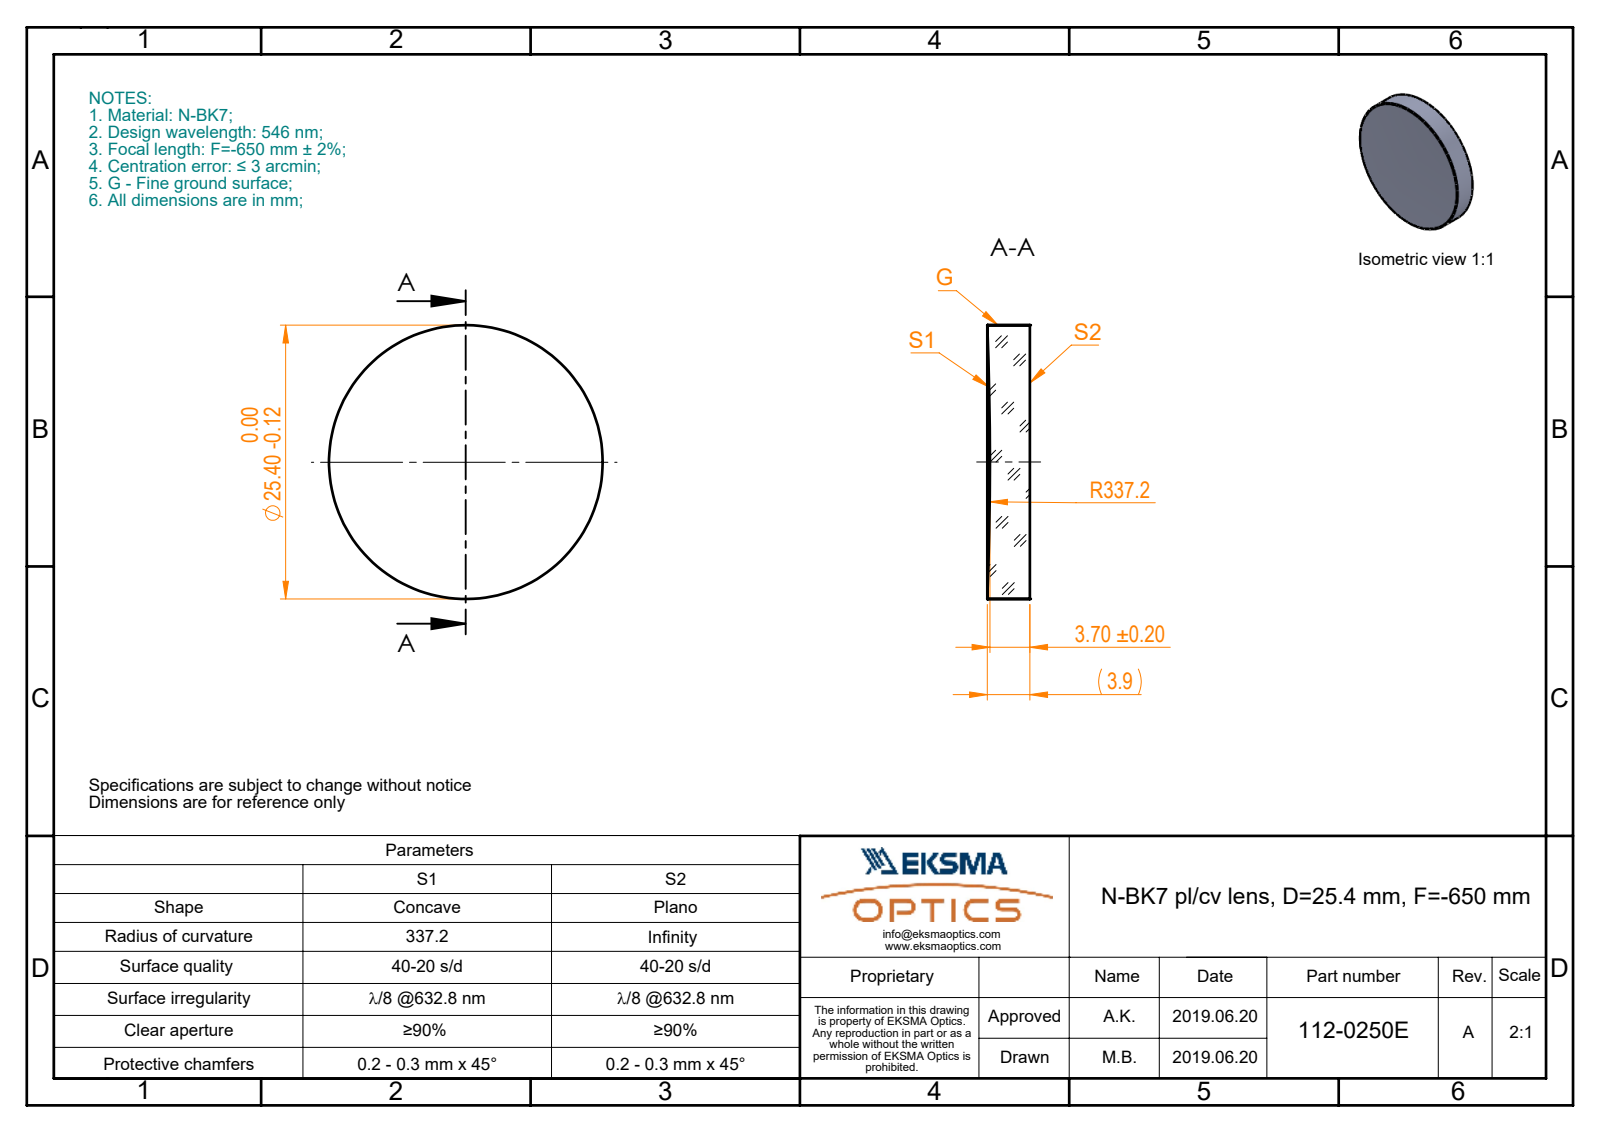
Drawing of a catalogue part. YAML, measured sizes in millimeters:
part_name: "112-0250E BK7 pl-cv 25.4 F-650"
step_written_by: "SolidWorks 2017 (CONFIG_CONTROL_DESIGN)"
units: millimeters
bodies: {solids: 1, faces: 5, planar: 1, cylindrical: 2, other: 2}
overall_size: [25.4, 25.4, 3.94]
volume: 1935
surface_area: 1328
round_bosses_or_shafts:
  - {diameter: 25.4, count: 1}
